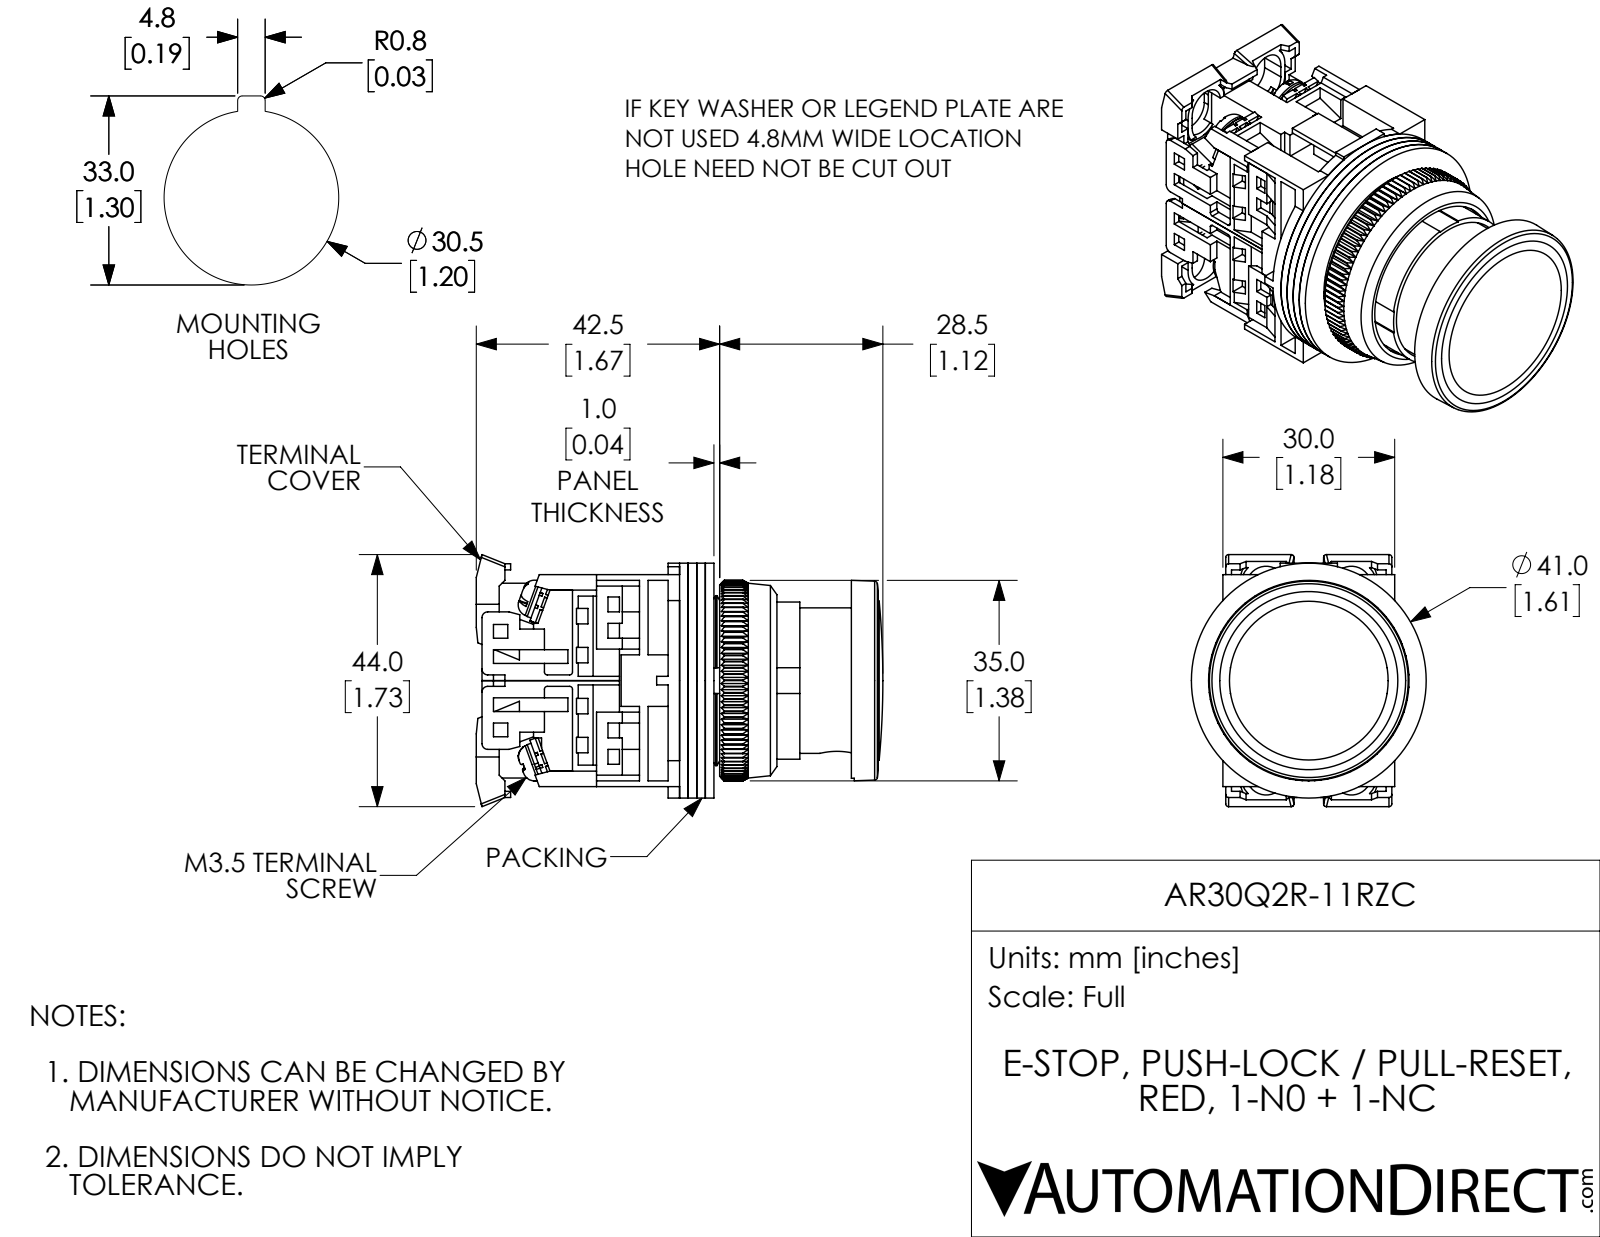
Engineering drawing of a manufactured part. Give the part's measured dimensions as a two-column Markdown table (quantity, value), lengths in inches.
| quantity | value |
| --- | --- |
| part name | AR30Q2R-11RZC |
| STEP written by | SolidWorks 2017 (AUTOMOTIVE_DESIGN) |
| units | inches |
| bodies | 25 solids, 1785 faces (1232 planar, 329 cylindrical, 224 other) |
| overall size | 2.795 × 1.732 × 1.614 |
| volume | 3.169 in³ |
| surface area | 69.65 in² |
| round holes (diameter × count) | 0.138 × 4, 0.142 × 4, 0.102 × 1, 0.114 × 1, 0.118 × 1, 0.236 × 1, 0.512 × 1, 0.63 × 1, 0.803 × 1, 0.937 × 1, 1.024 × 1, 1.122 × 1 |
| round bosses / shafts (diameter × count) | 0.26 × 4, 0.138 × 4, 1.614 × 1, 1.181 × 1, 1.083 × 1, 1 × 1, 0.787 × 1, 0.709 × 1 |
| partial cylindrical surfaces (radius × count) | 0.059 × 21, 0.02 × 12, 0.039 × 4, 0.138 × 4, 0.177 × 4, 0.118 × 2, 0.276 × 1, 0.398 × 1 |
| main face-to-face distances | 0.059, 0.118, 0.039, 0.177, 1.417, 0.079, 0.689, 1.358, 0.138, 0.02 |
| hole center spacings | 0.579, 0.61 |
